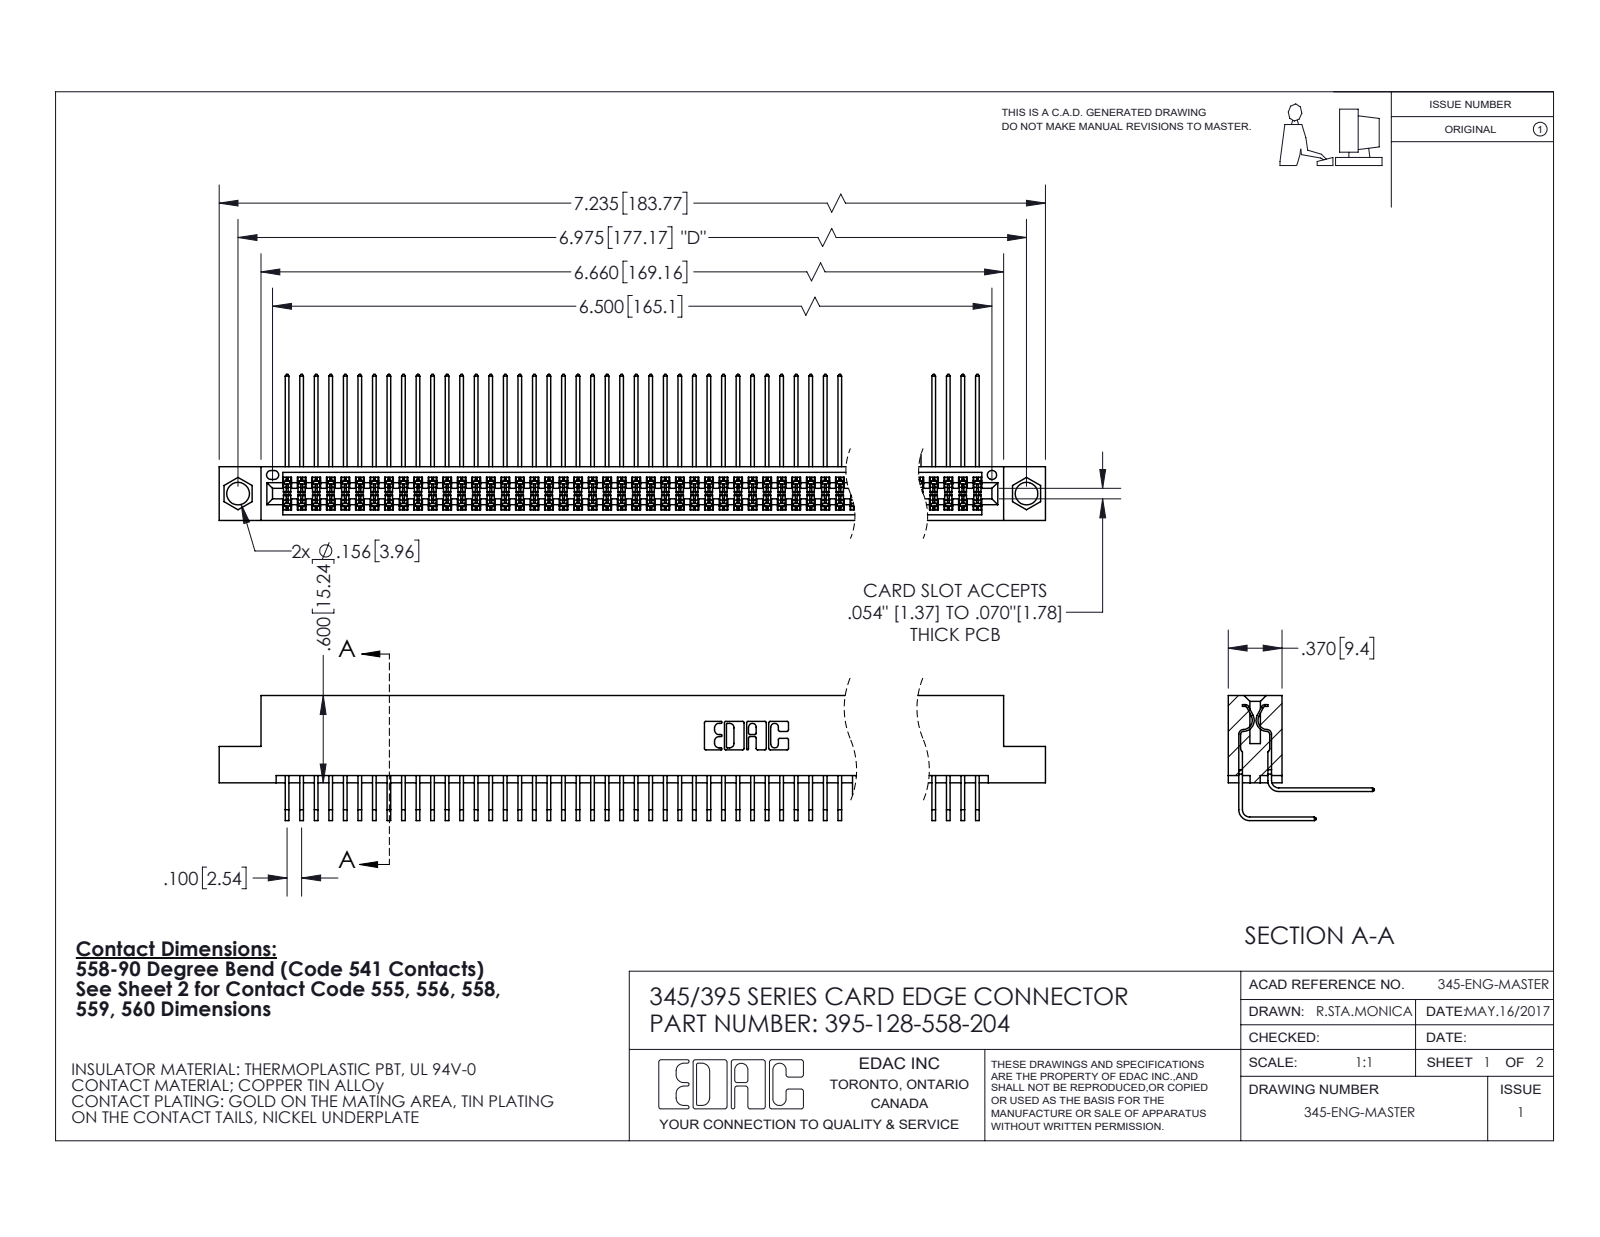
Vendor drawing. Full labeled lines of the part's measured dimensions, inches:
Part name (STEP PRODUCT): 395-128-558-204; 345-292-001_558 559 Tail - 1; 345-292-001_558 Tail - 2; 345 Part_Flush Mounting Lugs - 0.156 Dia-TI
STEP written by: SolidWorks 2020 (CONFIG_CONTROL_DESIGN)
Units: inches
Bodies: 129 solids, 6796 faces (4574 planar, 2222 cylindrical, 0 other)
Overall size (bounding box): 7.235 × 1.005 × 0.859
Volume: 1.14 in³ · Surface area: 48.63 in²
Round holes (diameter × count): ⌀0.156 ×2, ⌀0.064 ×1
Partial cylindrical surfaces — rounded edges, fillets, slot ends (radius × count): R0.006 ×192, R0.01 ×22, R0.007 ×6, R0.031 ×6, R0.026 ×3, R0.014 ×2, R0.019 ×2, R0.022 ×2
Main face-to-face distances: 0.072, 0.298, 0.2, 0.37, 0.098, 0.272, 0.025, 0.225, 0.025, 0.175
Hole centre spacings: 0.27, 6.739, 6.975
